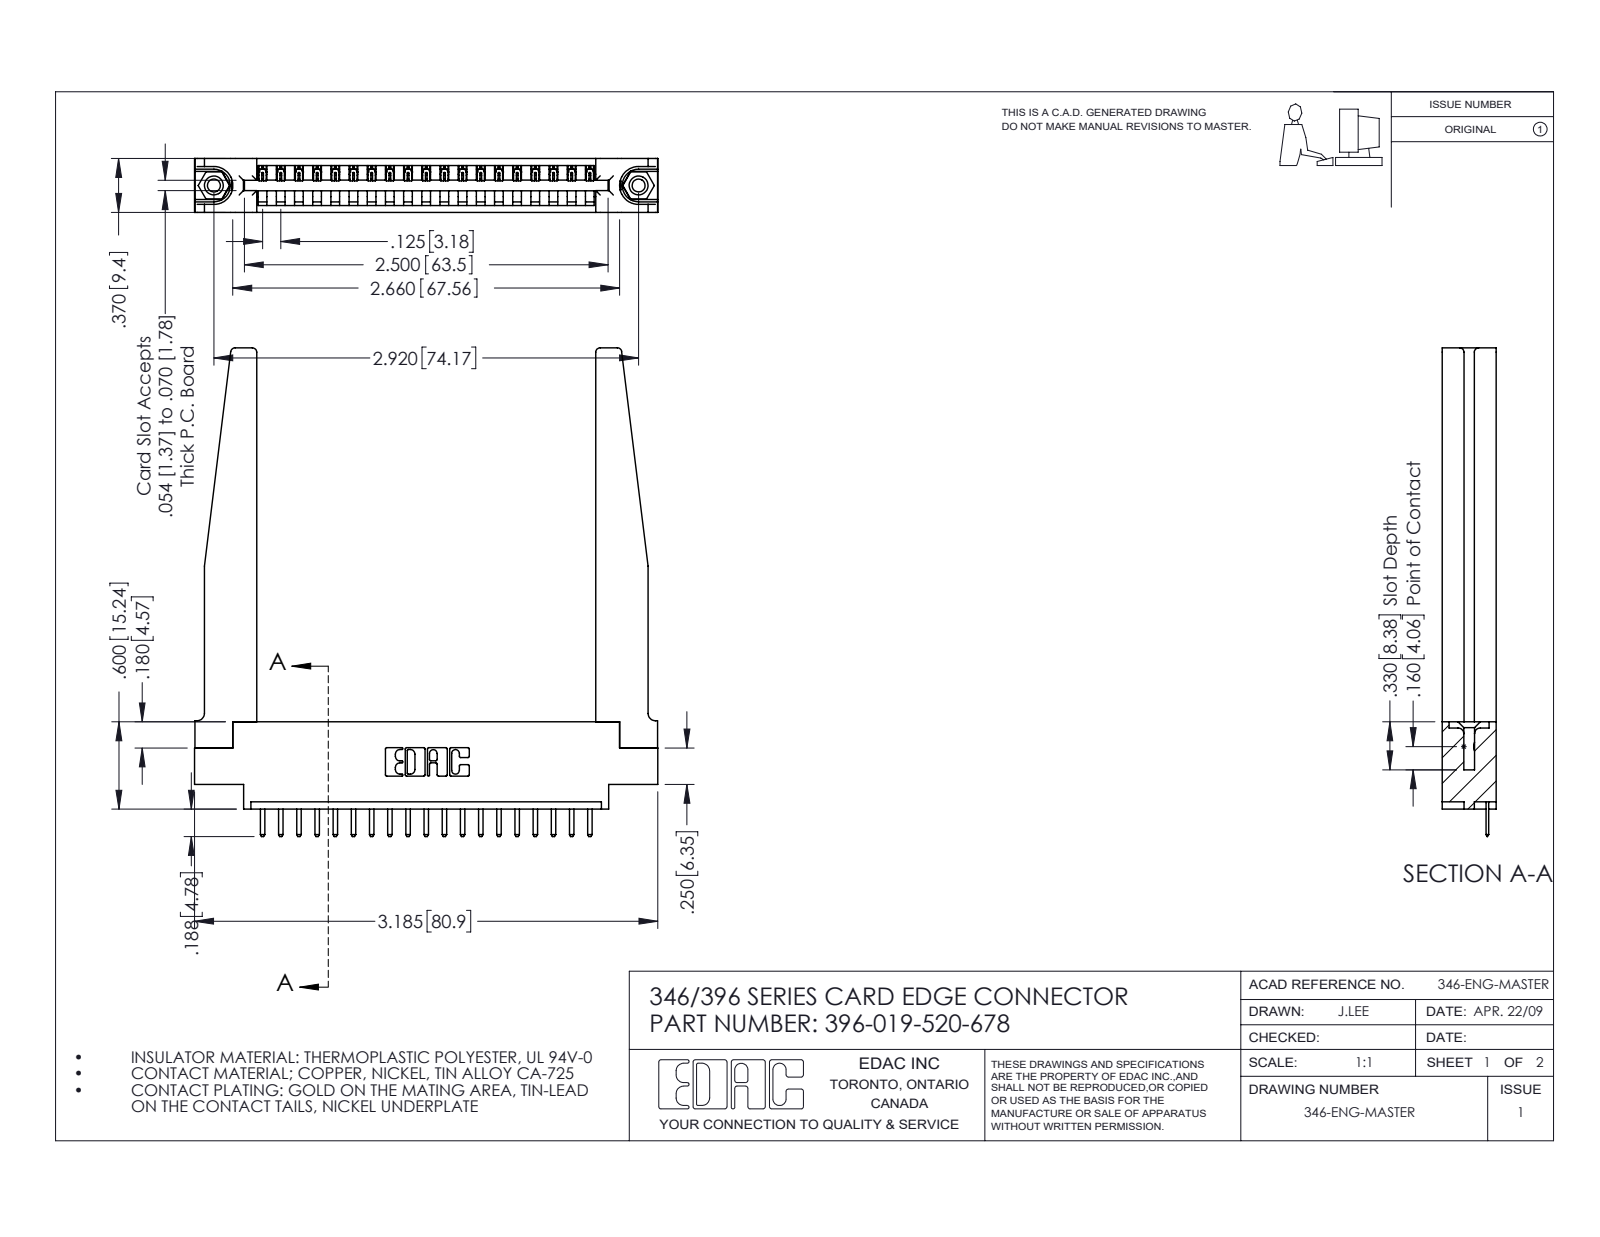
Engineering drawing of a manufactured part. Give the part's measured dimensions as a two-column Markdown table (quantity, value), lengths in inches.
| quantity | value |
| --- | --- |
| part name | 345-292-001_345-293-120; 346 Part_0.170 Offset - 0.156 Dia-TH; 396-019-520-678; 346-220-078_345-220-078 (+1 more) |
| STEP written by | SolidWorks 2016 (CONFIG_CONTROL_DESIGN) |
| units | inches |
| bodies | 24 solids, 1538 faces (1020 planar, 466 cylindrical, 52 other) |
| overall size | 3.358 × 3.185 × 0.37 |
| volume | 0.872 in³ |
| surface area | 24.01 in² |
| round holes (diameter × count) | 0.089 × 2, 0.125 × 2, 0.156 × 2, 0.064 × 1 |
| round bosses / shafts (diameter × count) | 0.155 × 2 |
| partial cylindrical surfaces (radius × count) | 0.01 × 40, 0.006 × 38, 0.01 × 22, 0.03 × 8, 0.007 × 6, 0.031 × 6, 0.026 × 3, 0.031 × 2 |
| main face-to-face distances | 0.37, 0.15, 0.072, 0.148, 0.048, 0.322, 0.25, 0.102, 0.22, 0.173 |
| hole center spacings | 0.246, 2.713, 2.92 |
